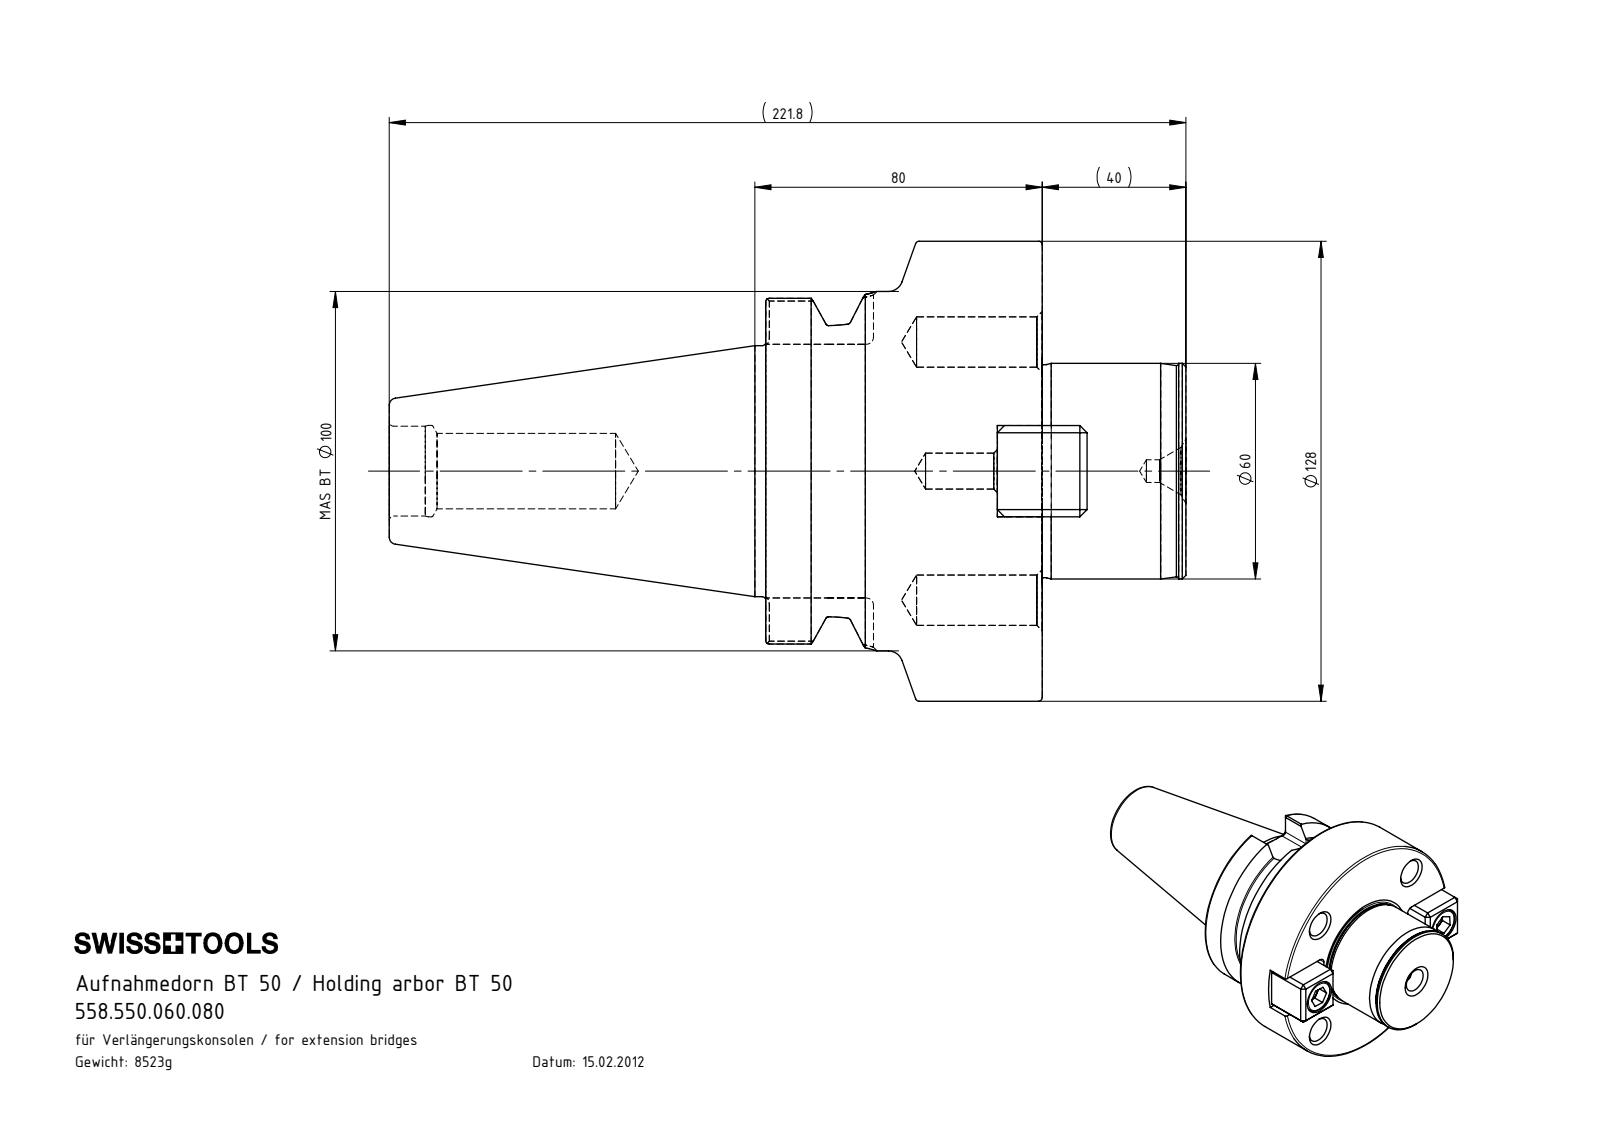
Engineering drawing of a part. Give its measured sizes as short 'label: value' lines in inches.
name: BT5-D60.K01.080
written by: SolidWorks 2017 (AUTOMOTIVE_DESIGN)
unit: in
bodies: 1 solid, 111 faces (27 planar, 34 cylindrical, 50 other)
size: 8.732 × 5.039 × 5.039
volume: 64.32 in³; area: 139.5 in²
holes: 4× ⌀0.551, 2× ⌀0.394, 1× ⌀0.248, 1× ⌀0.827, 1× ⌀0.984, 1× ⌀1.002
bosses: 1× ⌀5.039, 1× ⌀3.937, 1× ⌀3.346, 1× ⌀2.75, 1× ⌀2.362, 1× ⌀2.335
rounds: 8× R0.079, 4× R0.118, 1× R0.506
face distances: 3.031, 4.606, 1.575, 2.539, 0.492, 2.067, 0.89, 1.89, 1, 2.78
hole spacings: 1.505, 2, 2.828, 3.63, 1.929, 4, 3.858
